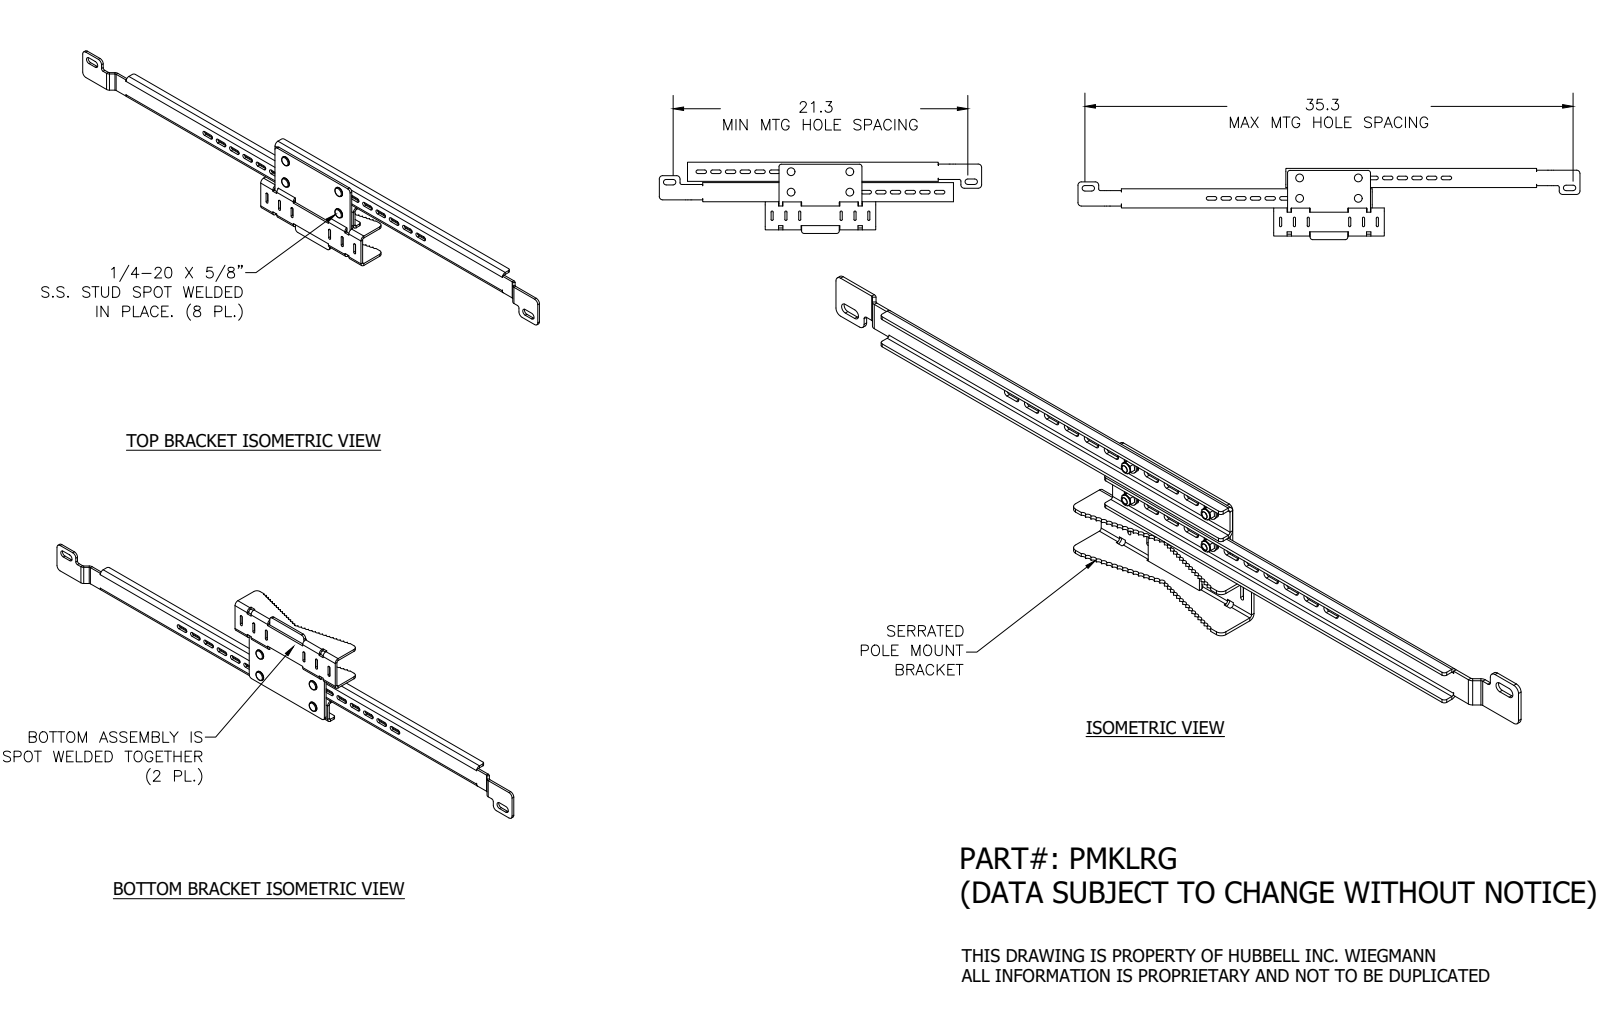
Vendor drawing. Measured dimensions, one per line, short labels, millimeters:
name: PMKLRG
written by: SolidWorks 2019 (AUTOMOTIVE_DESIGN)
unit: mm
bodies: 26 solids, 2042 faces (596 planar, 257 cylindrical, 1189 other)
size: 922.7 × 432.4 × 130.9
volume: 333 600 mm³; area: 251 600 mm²
holes: 4× ⌀5, 4× ⌀6.4, 4× ⌀7.4, 2× ⌀7.8, 1× ⌀8.5, 1× ⌀8.5, 1× ⌀9.5, 1× ⌀9.5
bosses: 4× ⌀14.3, 4× ⌀11, 4× ⌀6.4, 2× ⌀27.3, 2× ⌀15.9, 2× ⌀15.9, 2× ⌀14.3, 1× ⌀28.6
rounds: 44× R3.3, 39× R3.2, 14× R0.6, 12× R1.9, 10× R2.4, 10× R5.8, 10× R6.4, 4× R0.8
face distances: 3.4, 3.4, 6.8, 37.5, 31.8, 48.2, 28.3, 69.2, 40.9, 35.2
hole spacings: 108, 37.5, 37.5, 114.3, 114.3, 388.8, 388.8, 496.6
